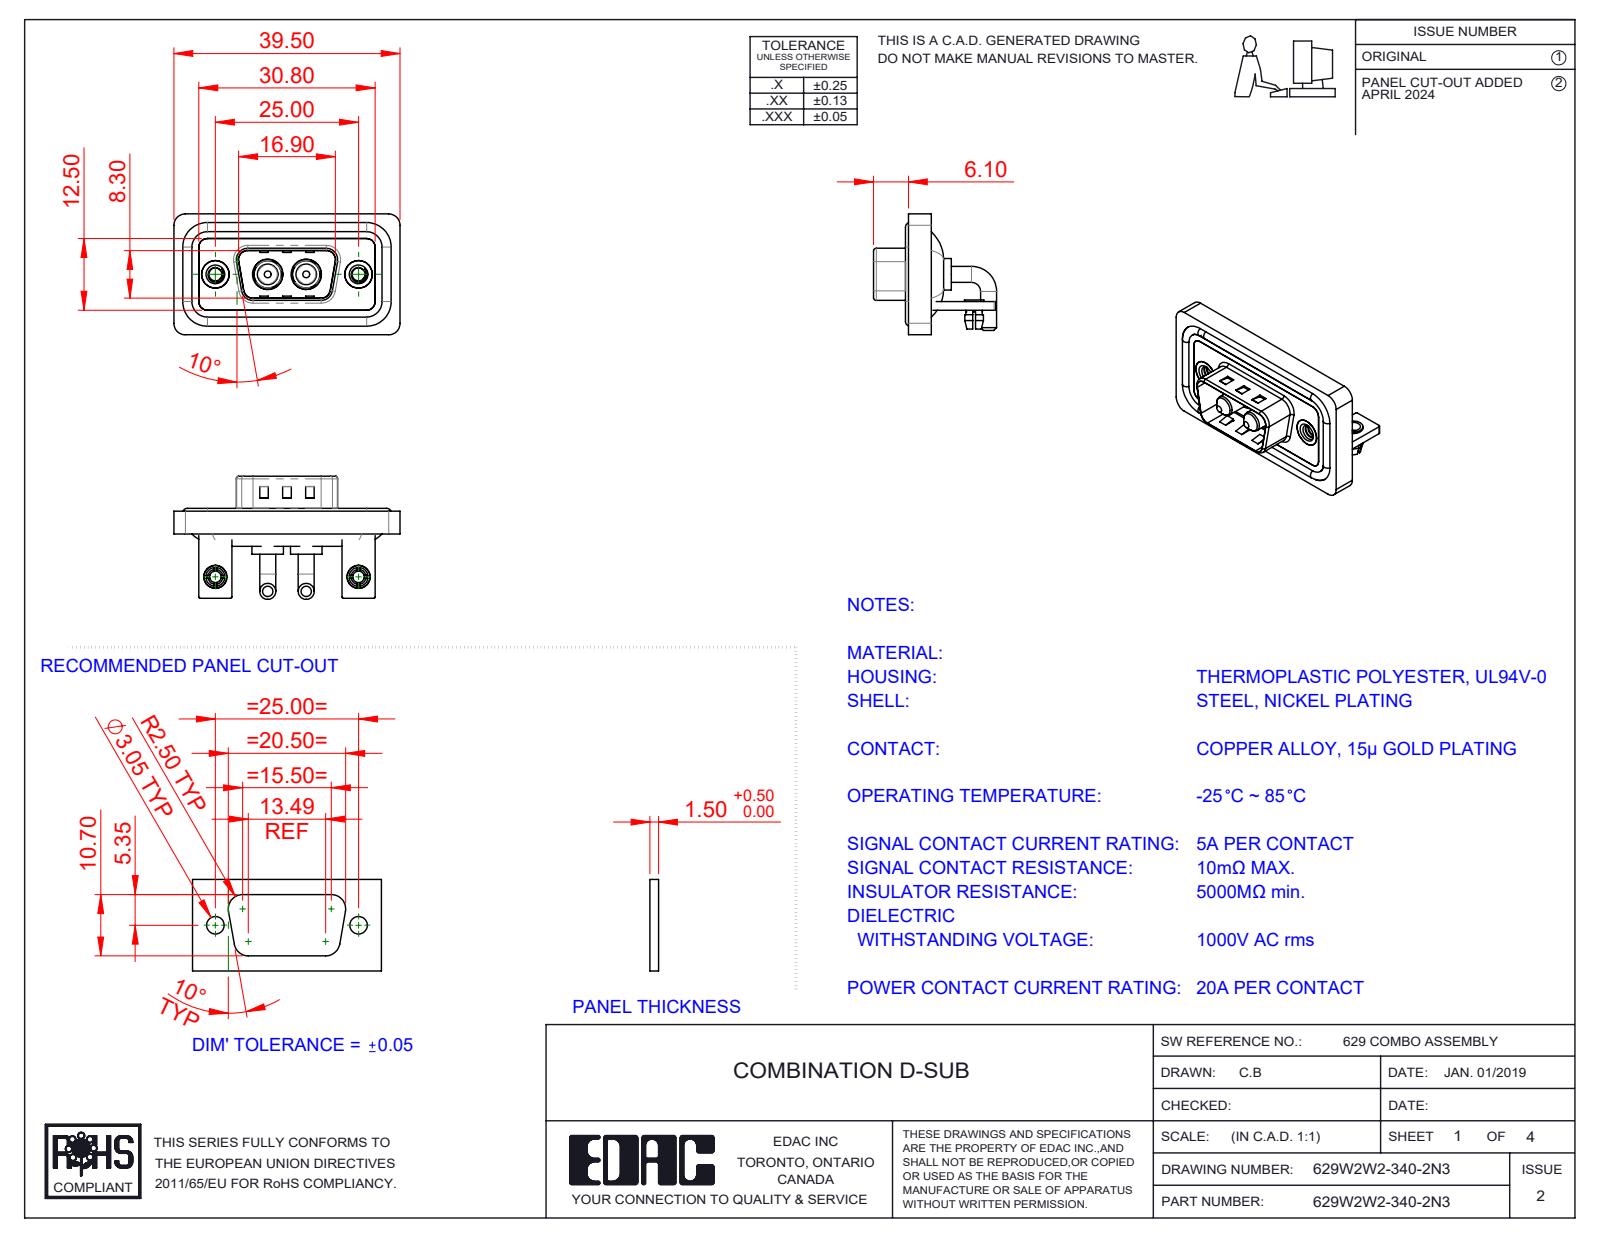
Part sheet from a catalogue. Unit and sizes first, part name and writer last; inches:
Units: inches
Overall size (bounding box): 1.555 × 0.846 × 0.831
Round holes (diameter × count): ⌀0.079 ×2, ⌀0.089 ×2, ⌀0.098 ×2, ⌀0.126 ×2, ⌀0.157 ×2, ⌀0.189 ×2, ⌀0.191 ×2, ⌀0.197 ×2, ⌀0.209 ×2
Round bosses / shafts (diameter × count): ⌀0.11 ×4, ⌀0.063 ×4, ⌀0.217 ×2, ⌀0.205 ×2, ⌀0.193 ×2, ⌀0.187 ×2, ⌀0.157 ×2, ⌀0.148 ×2
Partial cylindrical surfaces — rounded edges, fillets, slot ends (radius × count): R0.079 ×19, R0.059 ×18, R0.01 ×16, R0.02 ×9, R0.063 ×8, R0.024 ×4, R0.026 ×4, R0.035 ×4
Main face-to-face distances: 0.016, 0.059, 0.114, 0.031, 0.043, 0.047, 0.083, 0.063, 0.146, 0.098
Hole centre spacings: 0.36, 0.624, 0.984, 0.265
Volume: 0.299 in³ · Surface area: 12.34 in²
Bodies: 15 solids, 629 faces (233 planar, 272 cylindrical, 124 other)
Part name (STEP PRODUCT): 629Combo Waterproof Housing_09 Contacts; 629Combo Housing_2W2; 629W2W2-340-2N3; 629Combo Shell Front_09 Contacts (+5 more)
STEP written by: SolidWorks 2023 (CONFIG_CONTROL_DESIGN)
